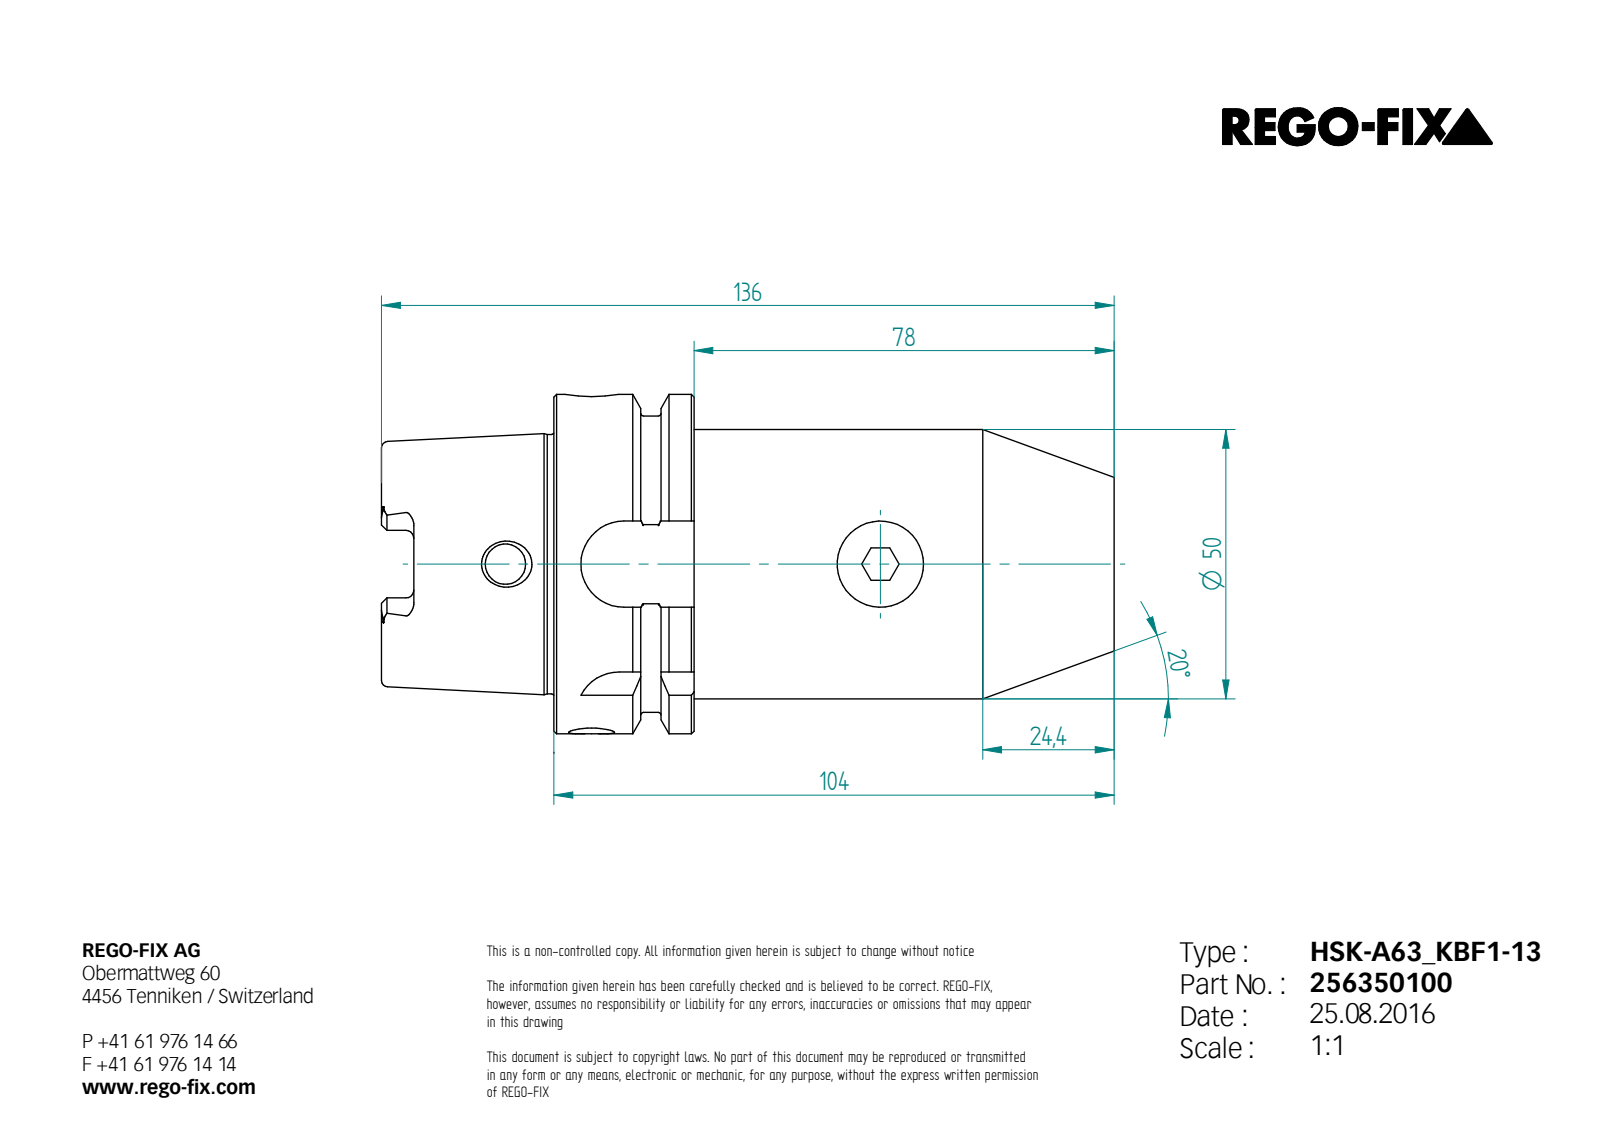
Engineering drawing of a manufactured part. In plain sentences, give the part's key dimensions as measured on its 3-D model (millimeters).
Its 3-D file was written by "Unknown (AUTOMOTIVE_DESIGN)". It is 1 solid with 142 faces: 53 planar, 39 cylindrical and 50 other. Overall it measures 136 by 63 by 63 millimeters. Its volume is 218 081 cubic millimeters and its surface area 33 912 square millimeters. Round holes: 6 of diameter 3, 1 of diameter 7.5, 1 of diameter 8.4, 1 of diameter 8.5, 1 of diameter 10, 1 of diameter 16, 1 of diameter 16.92, 1 of diameter 20, 1 of diameter 34, 1 of diameter 40. Round bosses or shafts: 1 of diameter 63, 1 of diameter 55, 1 of diameter 50, 1 of diameter 48.13. Partial cylindrical surfaces (rounded edges, fillets, slot ends): 6 of radius 1.5, 4 of radius 2.88, 4 of radius 8. The main face-to-face distances are 26, 104, 78, 10, 16, 94, 32, 53, 22, 12. The hole center spacings are 20, 3.48, 3.49, 6.94, 22.95, 25.71, 28.29, 25.72.
